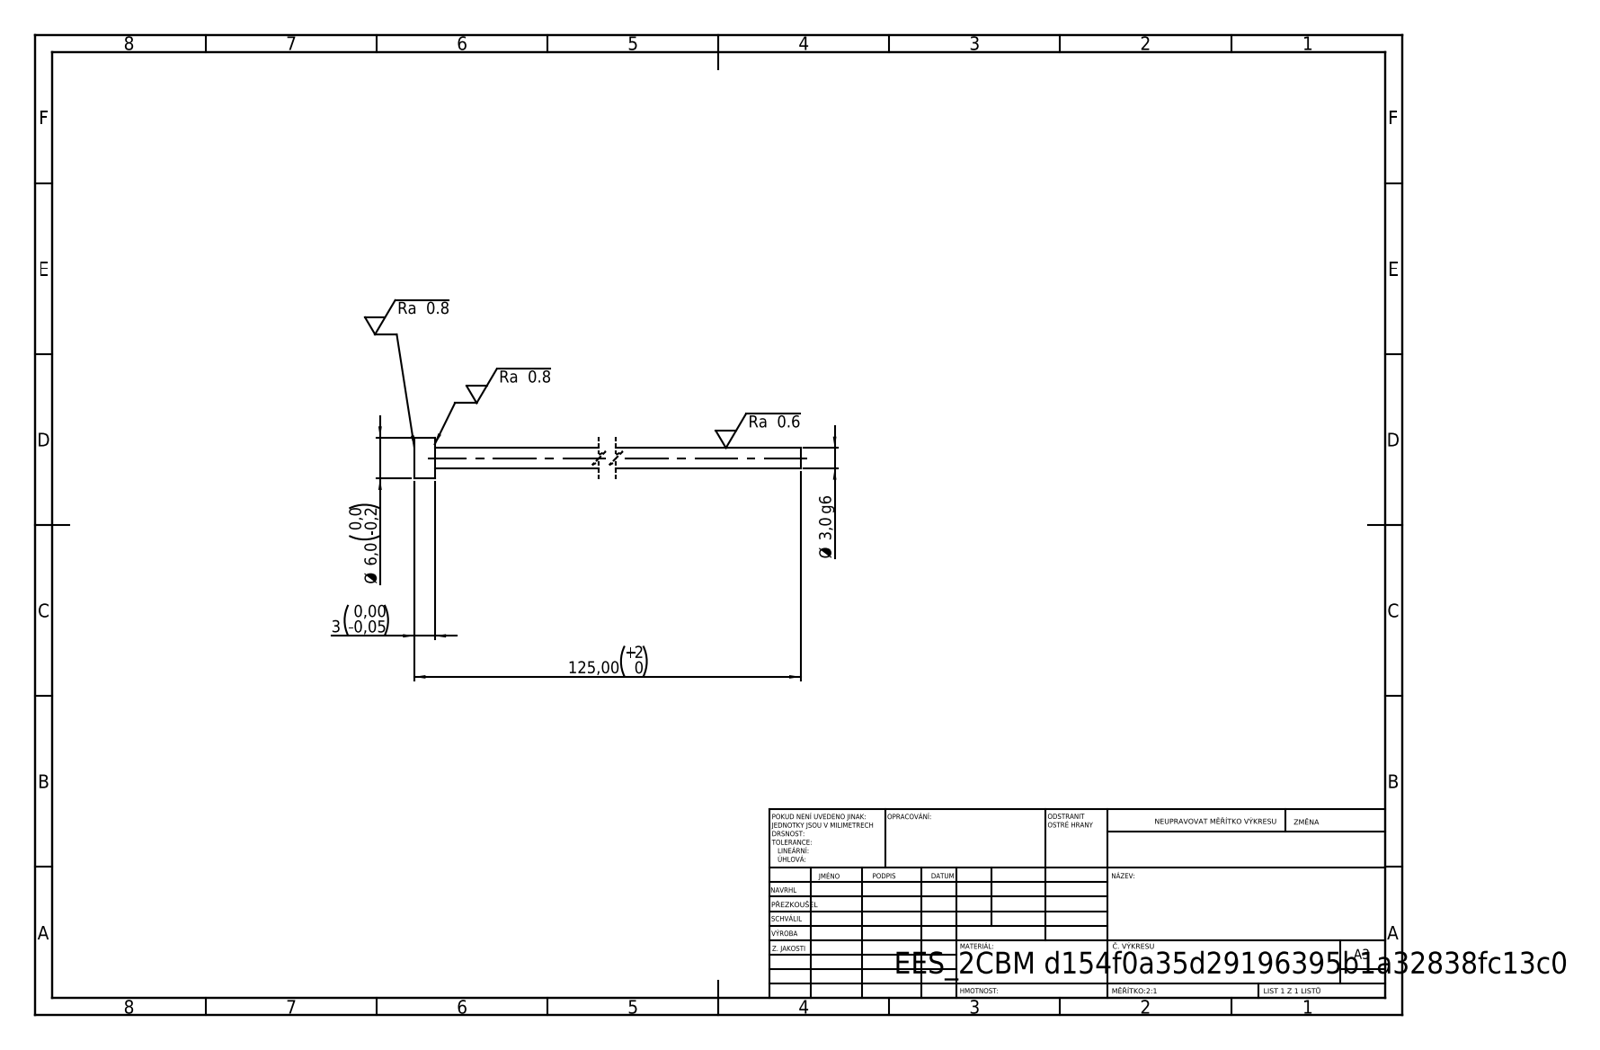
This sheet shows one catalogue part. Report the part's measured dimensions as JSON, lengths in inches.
{"step_written_by": "SolidWorks 2019 (CONFIG_CONTROL_DESIGN)", "units": "inches", "bodies": {"solids": 1, "faces": 7, "planar": 3, "cylindrical": 4, "other": 0}, "overall_size": [4.921, 0.236, 0.236], "volume_in3": 0.058, "surface_area_in2": 1.958, "round_bosses_or_shafts": [[0.236, 1], [0.118, 1]], "face_to_face_distances": [0.118, 4.921, 4.803]}
